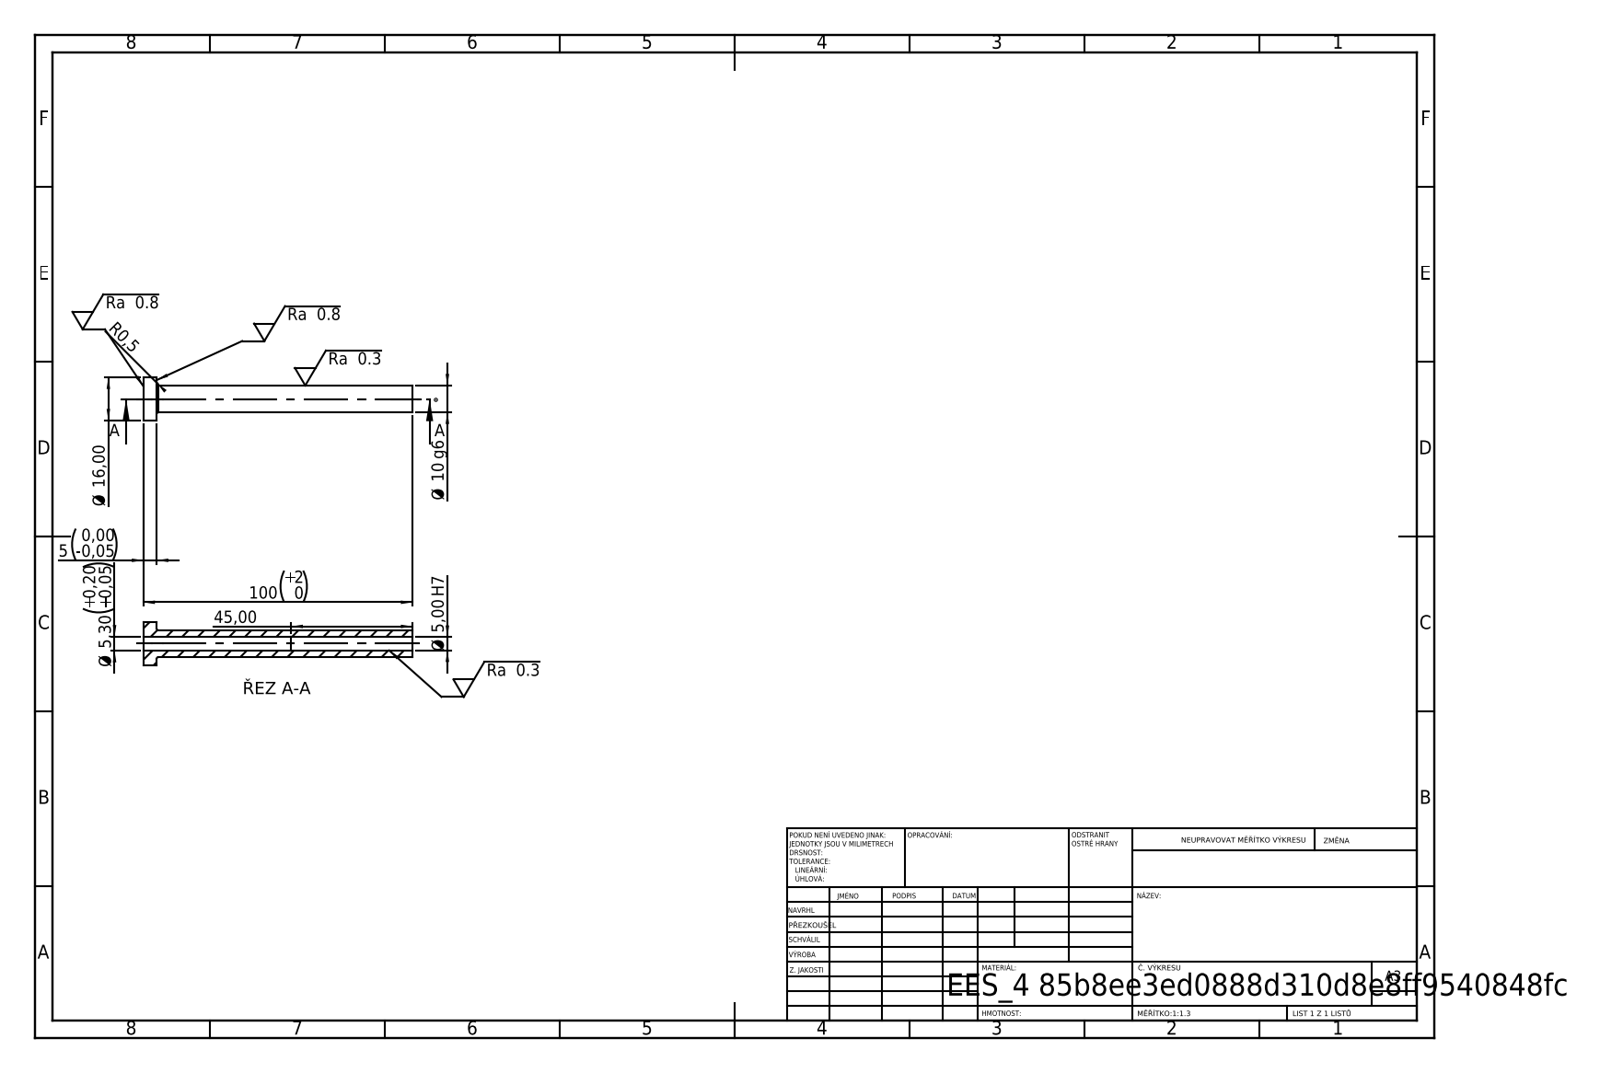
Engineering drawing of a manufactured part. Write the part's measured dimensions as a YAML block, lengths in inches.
step_written_by: "SolidWorks 2019 (CONFIG_CONTROL_DESIGN)"
units: inches
bodies: {solids: 1, faces: 14, planar: 4, cylindrical: 8, other: 2}
overall_size: [3.937, 0.63, 0.63]
volume: 0.389
surface_area: 8.083
round_holes:
  - {diameter: 0.197, count: 1}
  - {diameter: 0.209, count: 1}
round_bosses_or_shafts:
  - {diameter: 0.63, count: 1}
  - {diameter: 0.394, count: 1}
face_to_face_distances: [0.197, 3.937, 3.74, 2.165, 1.969, 1.772]
